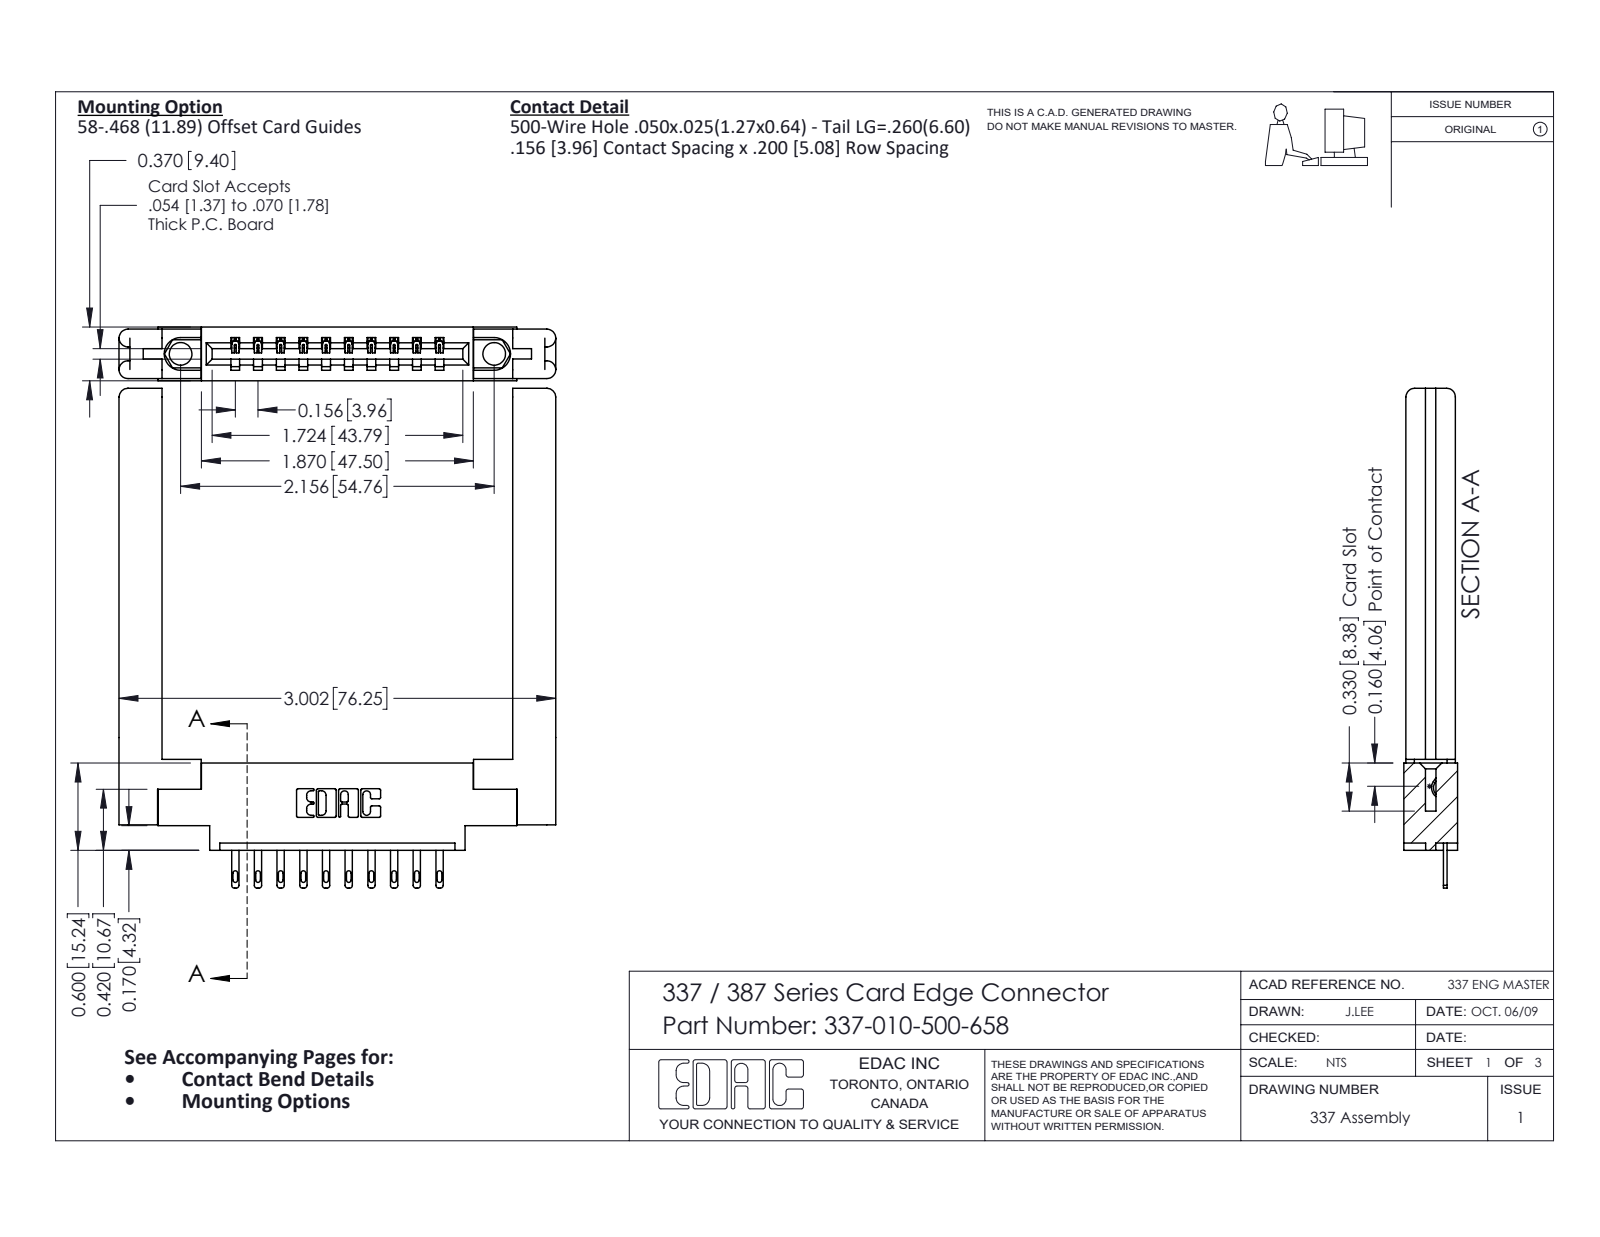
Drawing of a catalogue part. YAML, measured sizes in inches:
part_name: "307-220-058; 345-292-001_345-293-100; 337-010-500-658; 345-250-001_345-250-001-102 (+1 more)"
step_written_by: "SolidWorks 2016 (CONFIG_CONTROL_DESIGN)"
units: inches
bodies: {solids: 15, faces: 840, planar: 558, cylindrical: 258, other: 24}
overall_size: [3.435, 3.002, 0.37]
volume: 0.889
surface_area: 19.86
round_holes:
  - {diameter: 0.089, count: 2}
  - {diameter: 0.125, count: 2}
  - {diameter: 0.156, count: 2}
round_bosses_or_shafts:
  - {diameter: 0.155, count: 2}
partial_cylinders:
  - {radius: 0.01, count: 22}
  - {radius: 0.006, count: 20}
  - {radius: 0.016, count: 20}
  - {radius: 0.02, count: 20}
  - {radius: 0.061, count: 8}
  - {radius: 0.007, count: 6}
  - {radius: 0.031, count: 6}
  - {radius: 0.06, count: 5}
face_to_face_distances: [0.355, 0.015, 0.34, 0.37, 0.15, 0.135, 0.22, 0.206, 0.072, 0.148]
hole_center_spacings: [2.156]
